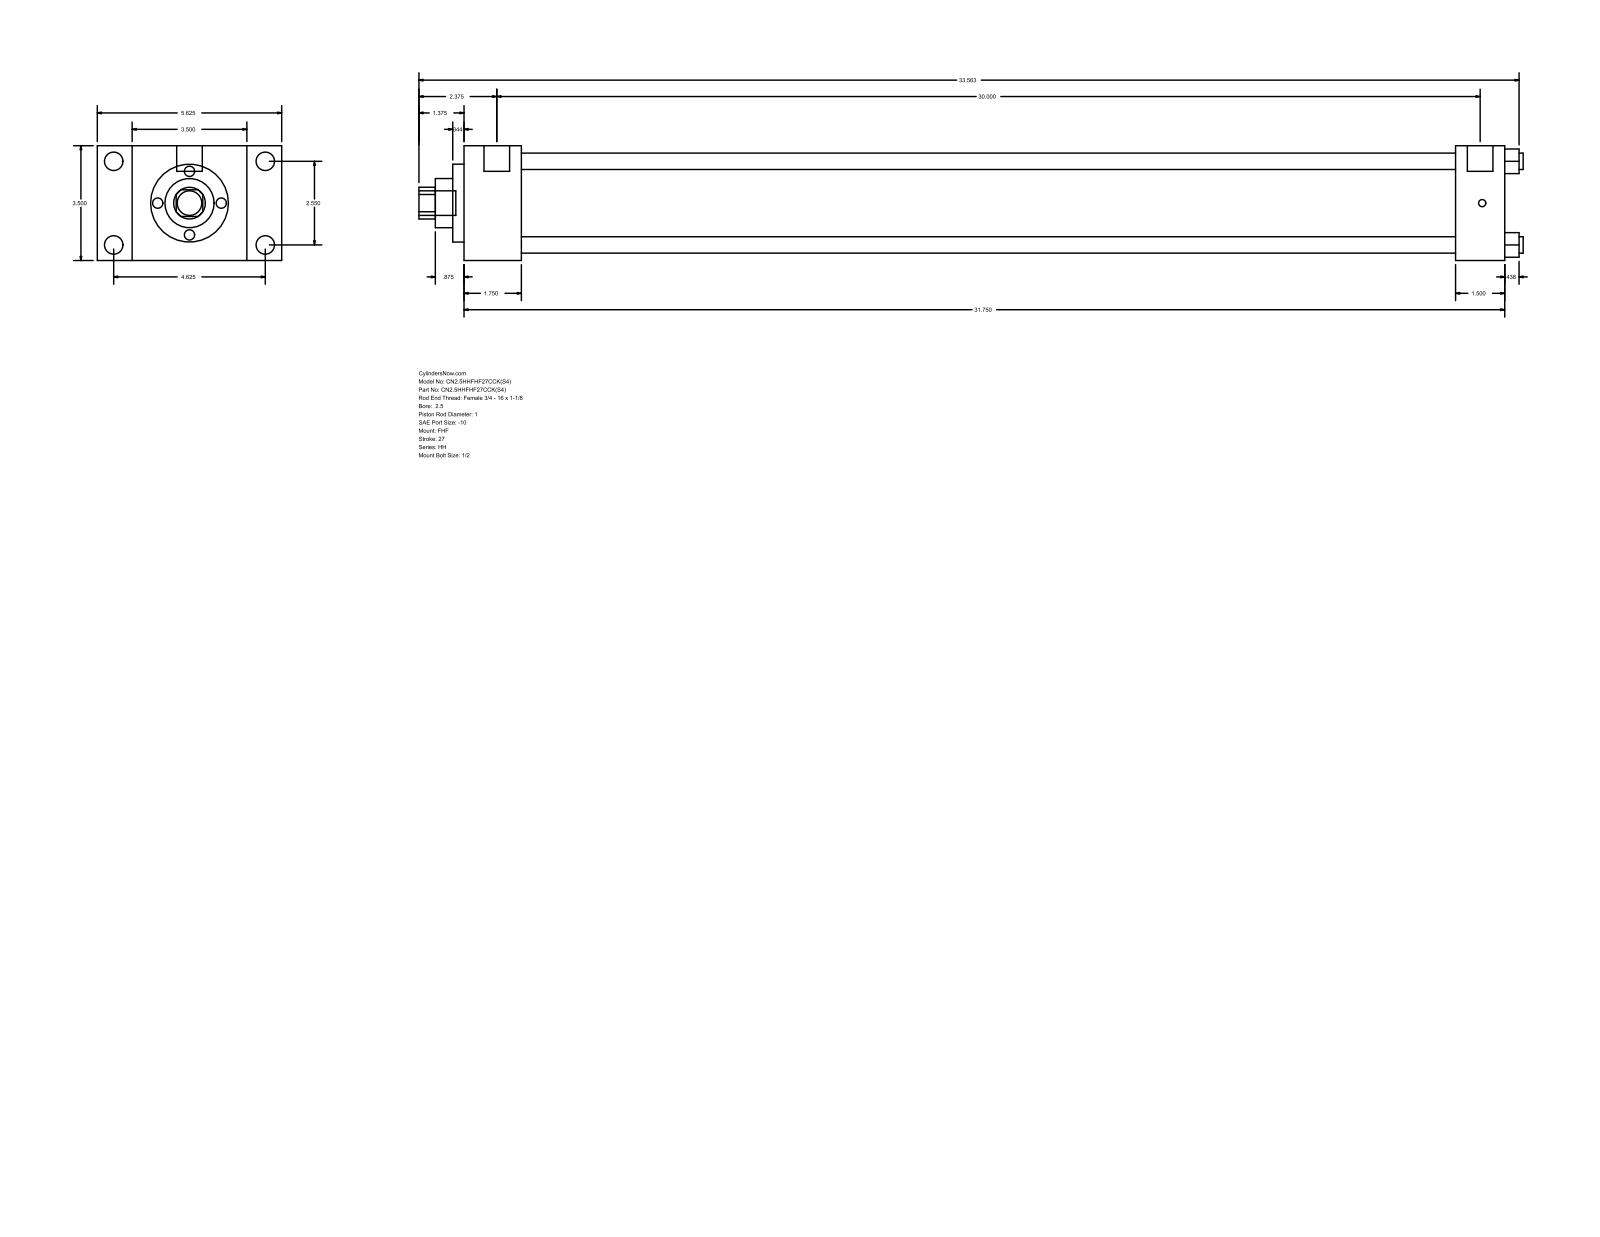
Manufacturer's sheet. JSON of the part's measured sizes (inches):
{"part_name": "HH_FHF__0250_1", "step_written_by": "GSSL Pune (CONFIG_CONTROL_DESIGN)", "units": "inches", "bodies": {"solids": 0, "faces": 90, "planar": 61, "cylindrical": 29, "other": 0}, "overall_size": [33.687, 5.625, 3.5], "round_holes": [[0.5, 4], [1, 1], [1.5, 1], [2.375, 1], [2.875, 1]], "round_bosses_or_shafts": [[0.563, 4], [0.219, 4], [0.781, 2], [0.75, 1]], "partial_cylinders_radius": [[0.484, 1]], "face_to_face_distances": [3.5, 1.75, 1.063, 4.563, 31.75, 30, 5.625, 30.25, 28.5, 1.5], "hole_center_spacings": [1.803, 2.55, 3.606]}
